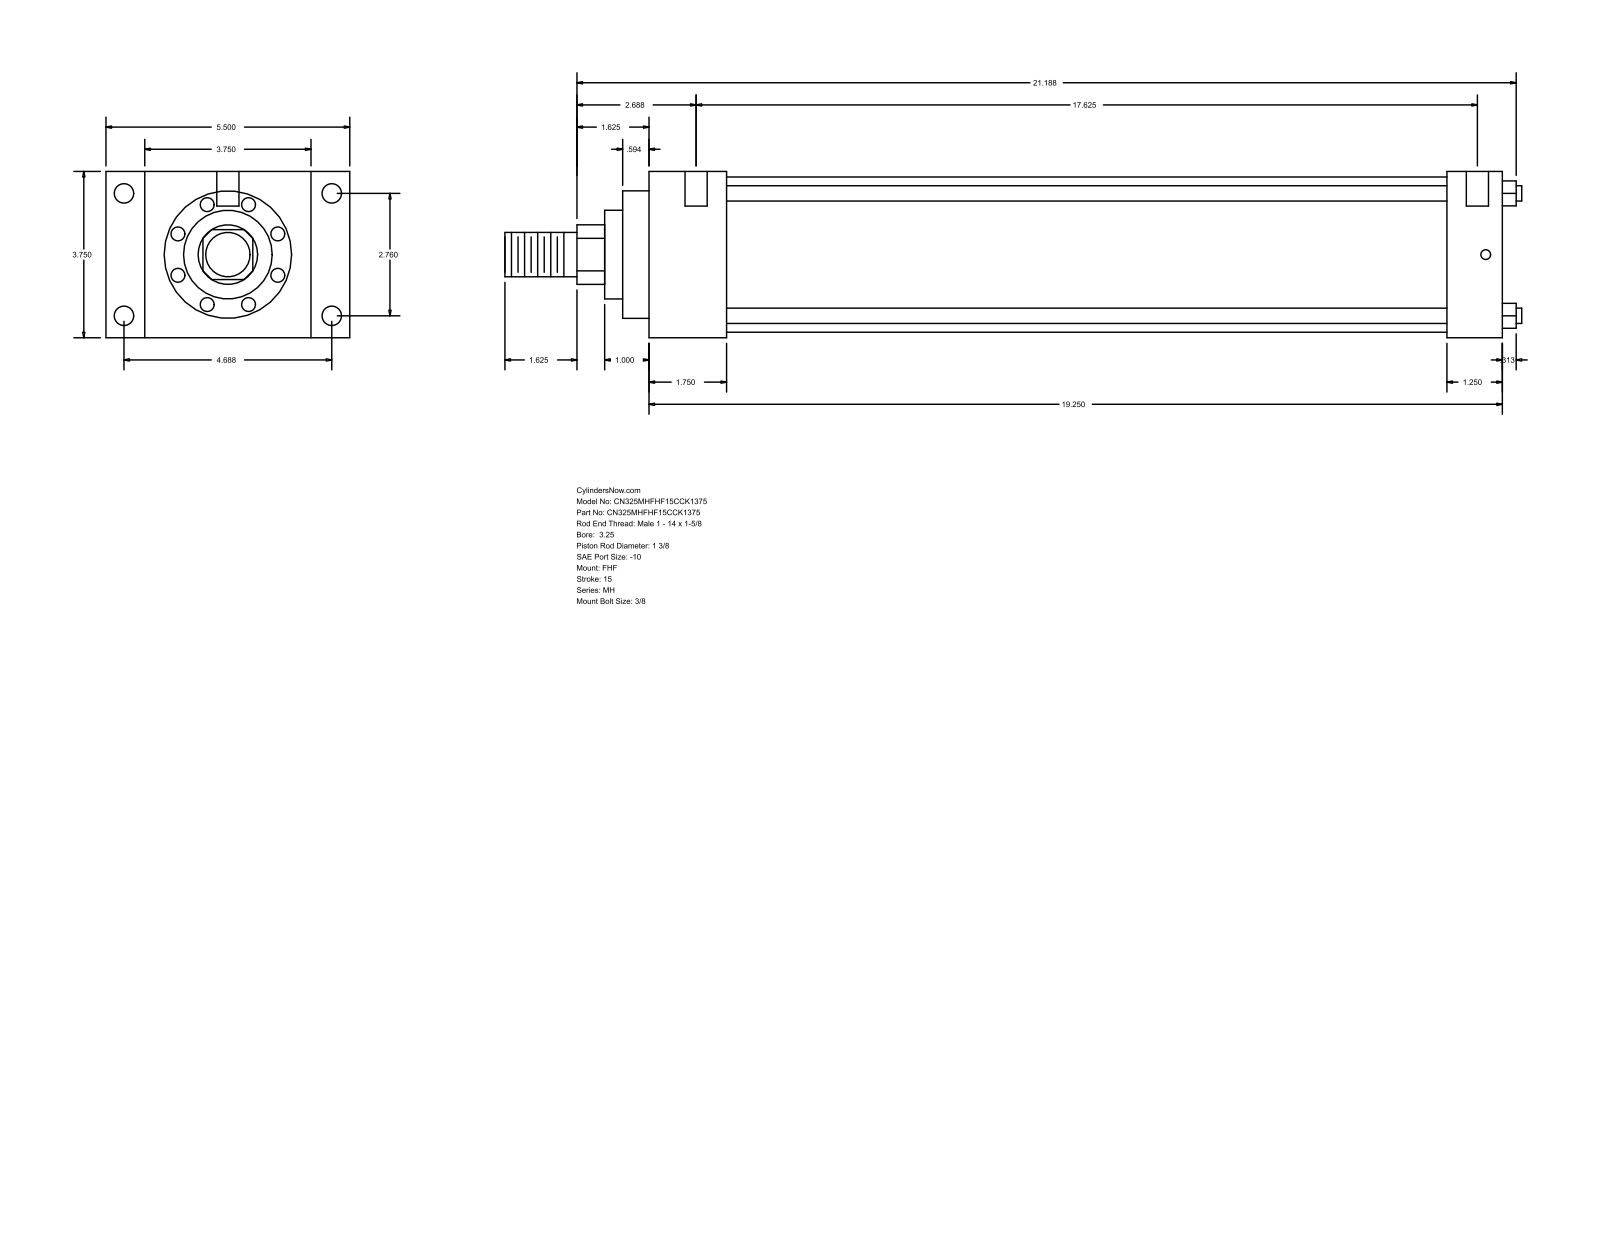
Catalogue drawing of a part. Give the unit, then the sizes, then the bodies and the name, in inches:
Units: inches
Overall size (bounding box): 22.937 × 5.5 × 3.75
Round holes (diameter × count): ⌀0.219 ×4, ⌀0.438 ×4, ⌀0.5 ×2
Round bosses / shafts (diameter × count): ⌀0.345 ×4, ⌀3.5 ×1, ⌀2.875 ×1, ⌀2 ×1, ⌀1.375 ×1, ⌀1 ×1
Partial cylindrical surfaces — rounded edges, fillets, slot ends (radius × count): R0.672 ×1
Main face-to-face distances: 3.75, 19.25, 1.75, 17.5, 0.875, 4.625, 5.5, 18, 16.25, 1.25
Hole centre spacings: 2.76, 4.687, 5.439, 17.875, 0.063, 0.187, 17.625, 17.688
Bodies: 0 solids, 90 faces (61 planar, 29 cylindrical, 0 other)
Part name (STEP PRODUCT): MH_FHF__0325_1.375
STEP written by: GSSL Pune (CONFIG_CONTROL_DESIGN)
